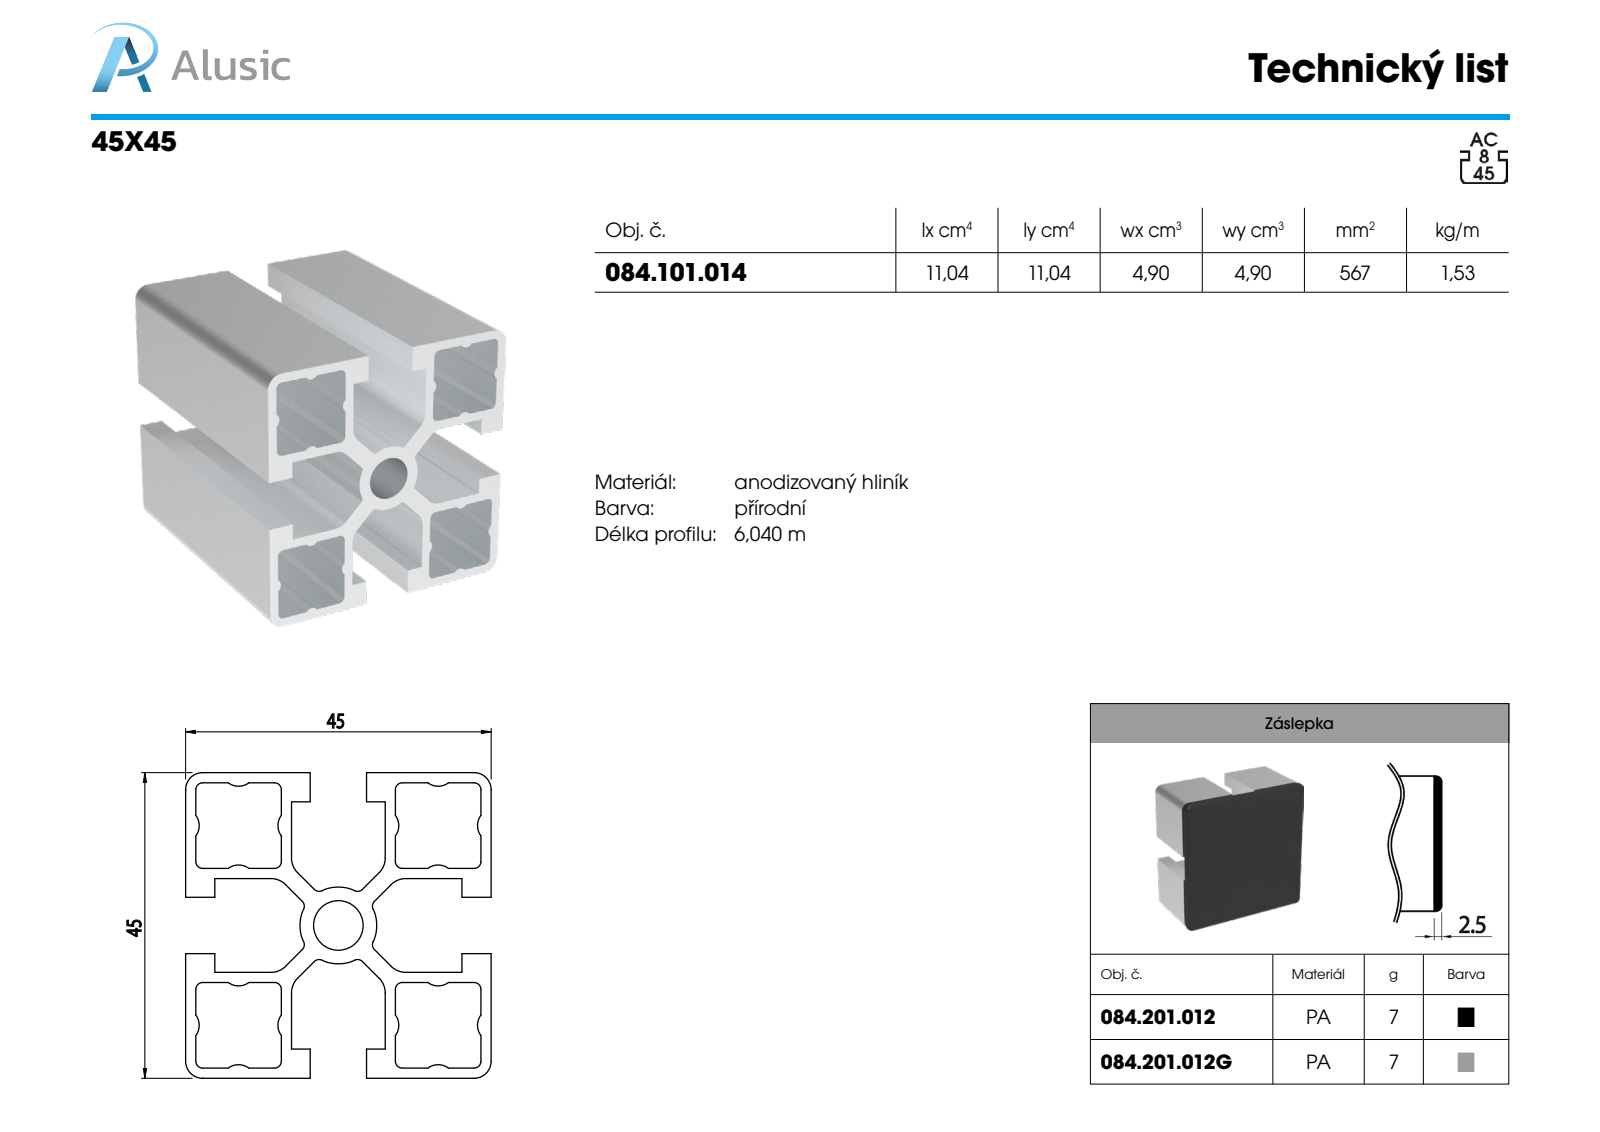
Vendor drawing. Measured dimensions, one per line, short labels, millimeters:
name: 084.101.014
written by: SolidWorks 2018 (AUTOMOTIVE_DESIGN)
unit: mm
bodies: 1 solid, 139 faces (74 planar, 65 cylindrical, 0 other)
size: 100 × 45 × 45
volume: 56 089 mm³; area: 57 447 mm²
holes: 1× ⌀7.3
rounds: 16× R1, 16× R1.25, 8× R0.5, 8× R3, 4× R2.5, 1× R5.65
face distances: 1.5, 14.1, 29.4, 43.5, 30.9, 12.6, 15.6, 27.9, 15.3, 45
